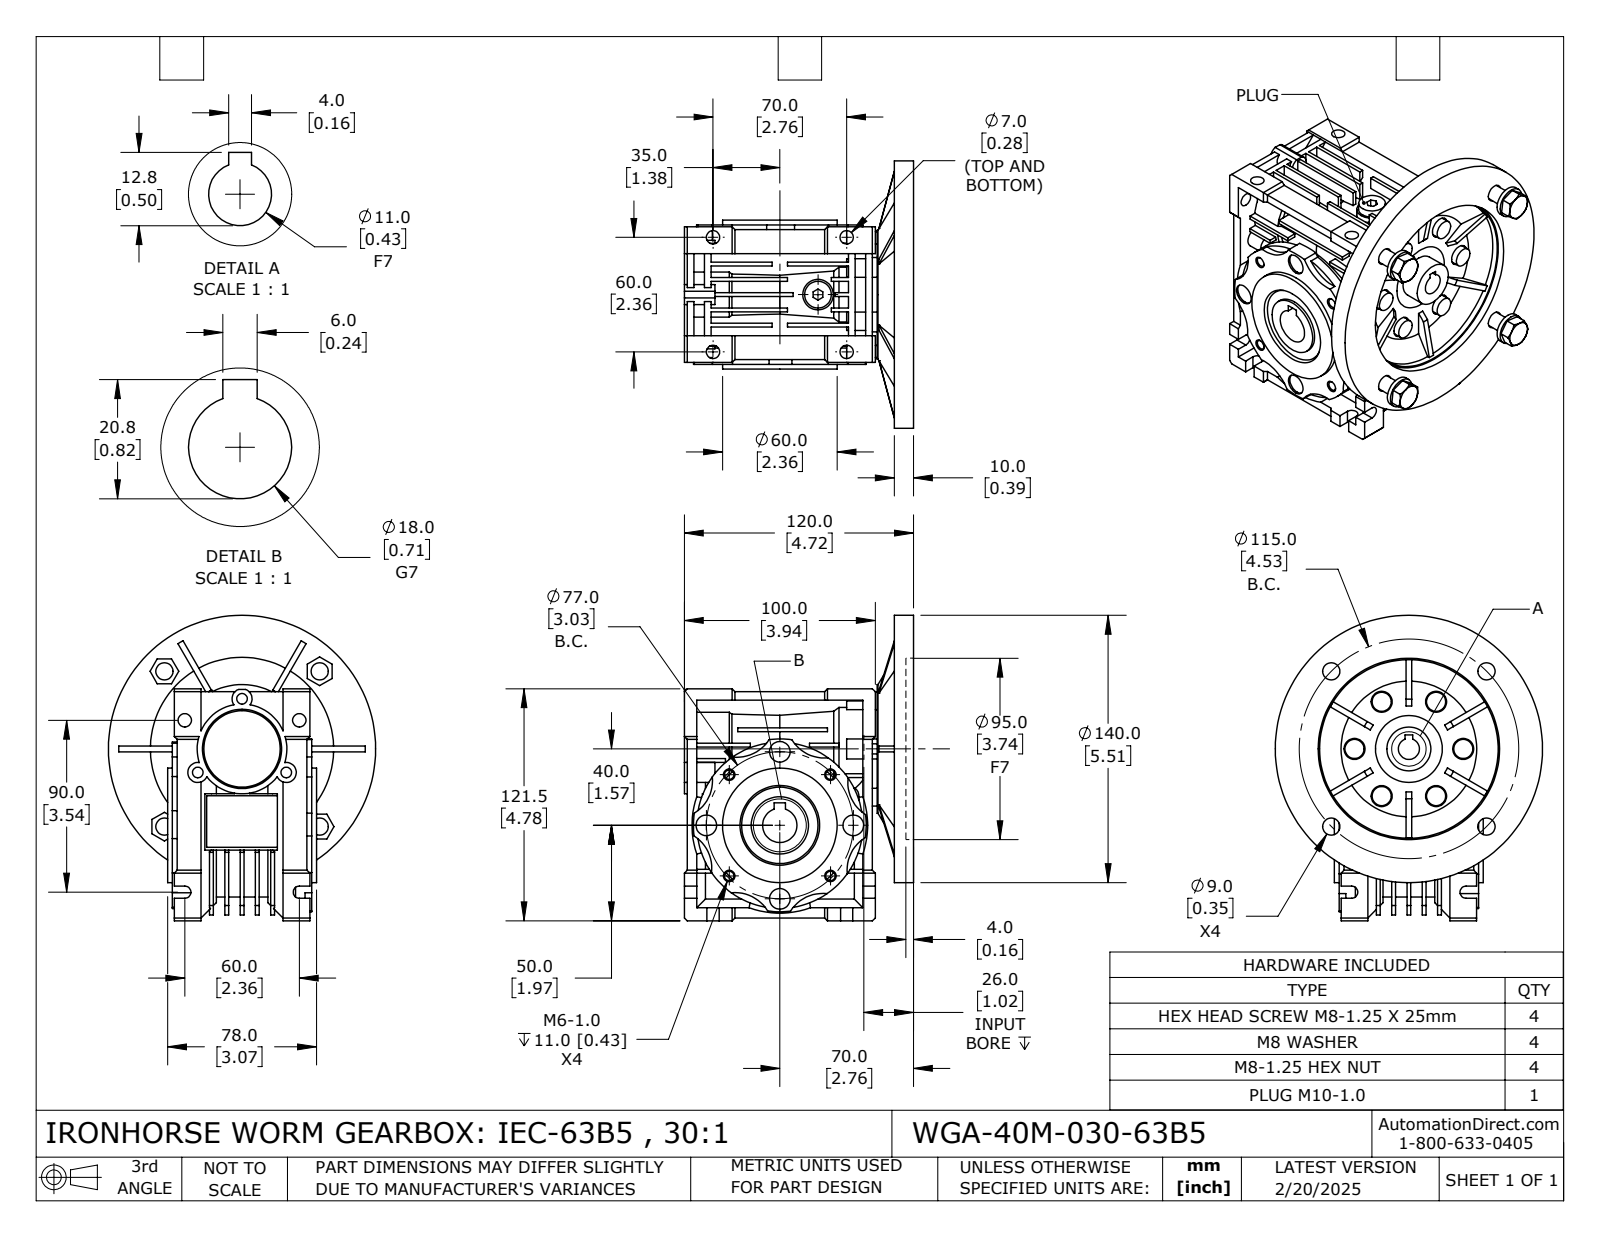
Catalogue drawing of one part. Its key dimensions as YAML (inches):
part_name: "WGA-40M-030-63B5"
step_written_by: "SolidWorks 2024 (CONFIG_CONTROL_DESIGN)"
units: inches
bodies: {solids: 18, faces: 1083, planar: 592, cylindrical: 298, other: 193}
overall_size: [6.299, 5.512, 5.432]
volume: 45.77
surface_area: 295.5
round_holes:
  - {diameter: 0.433, count: 7}
  - {diameter: 0.276, count: 6}
  - {diameter: 0.354, count: 5}
  - {diameter: 0.194, count: 4}
  - {diameter: 0.268, count: 4}
  - {diameter: 0.315, count: 4}
  - {diameter: 0.359, count: 4}
  - {diameter: 0.425, count: 4}
  - {diameter: 0.219, count: 3}
  - {diameter: 0.453, count: 1}
  - {diameter: 0.709, count: 1}
  - {diameter: 0.906, count: 1}
round_bosses_or_shafts:
  - {diameter: 0.394, count: 6}
  - {diameter: 0.63, count: 5}
  - {diameter: 5.512, count: 1}
  - {diameter: 2.953, count: 1}
  - {diameter: 2.657, count: 1}
  - {diameter: 2.362, count: 1}
  - {diameter: 2.126, count: 1}
  - {diameter: 1.85, count: 1}
partial_cylinders:
  - {radius: 0.787, count: 8}
  - {radius: 0.126, count: 6}
  - {radius: 0.206, count: 6}
  - {radius: 0.207, count: 3}
  - {radius: 1.713, count: 1}
  - {radius: 1.716, count: 1}
  - {radius: 1.781, count: 1}
  - {radius: 1.811, count: 1}
face_to_face_distances: [0.394, 0.315, 0.236, 0.079, 0.197, 0.059, 0.63, 0.945, 0.551, 0.098]
hole_center_spacings: [1.122, 1.146, 2.765, 1.943, 1.215, 1.32, 1.476, 1.516]
